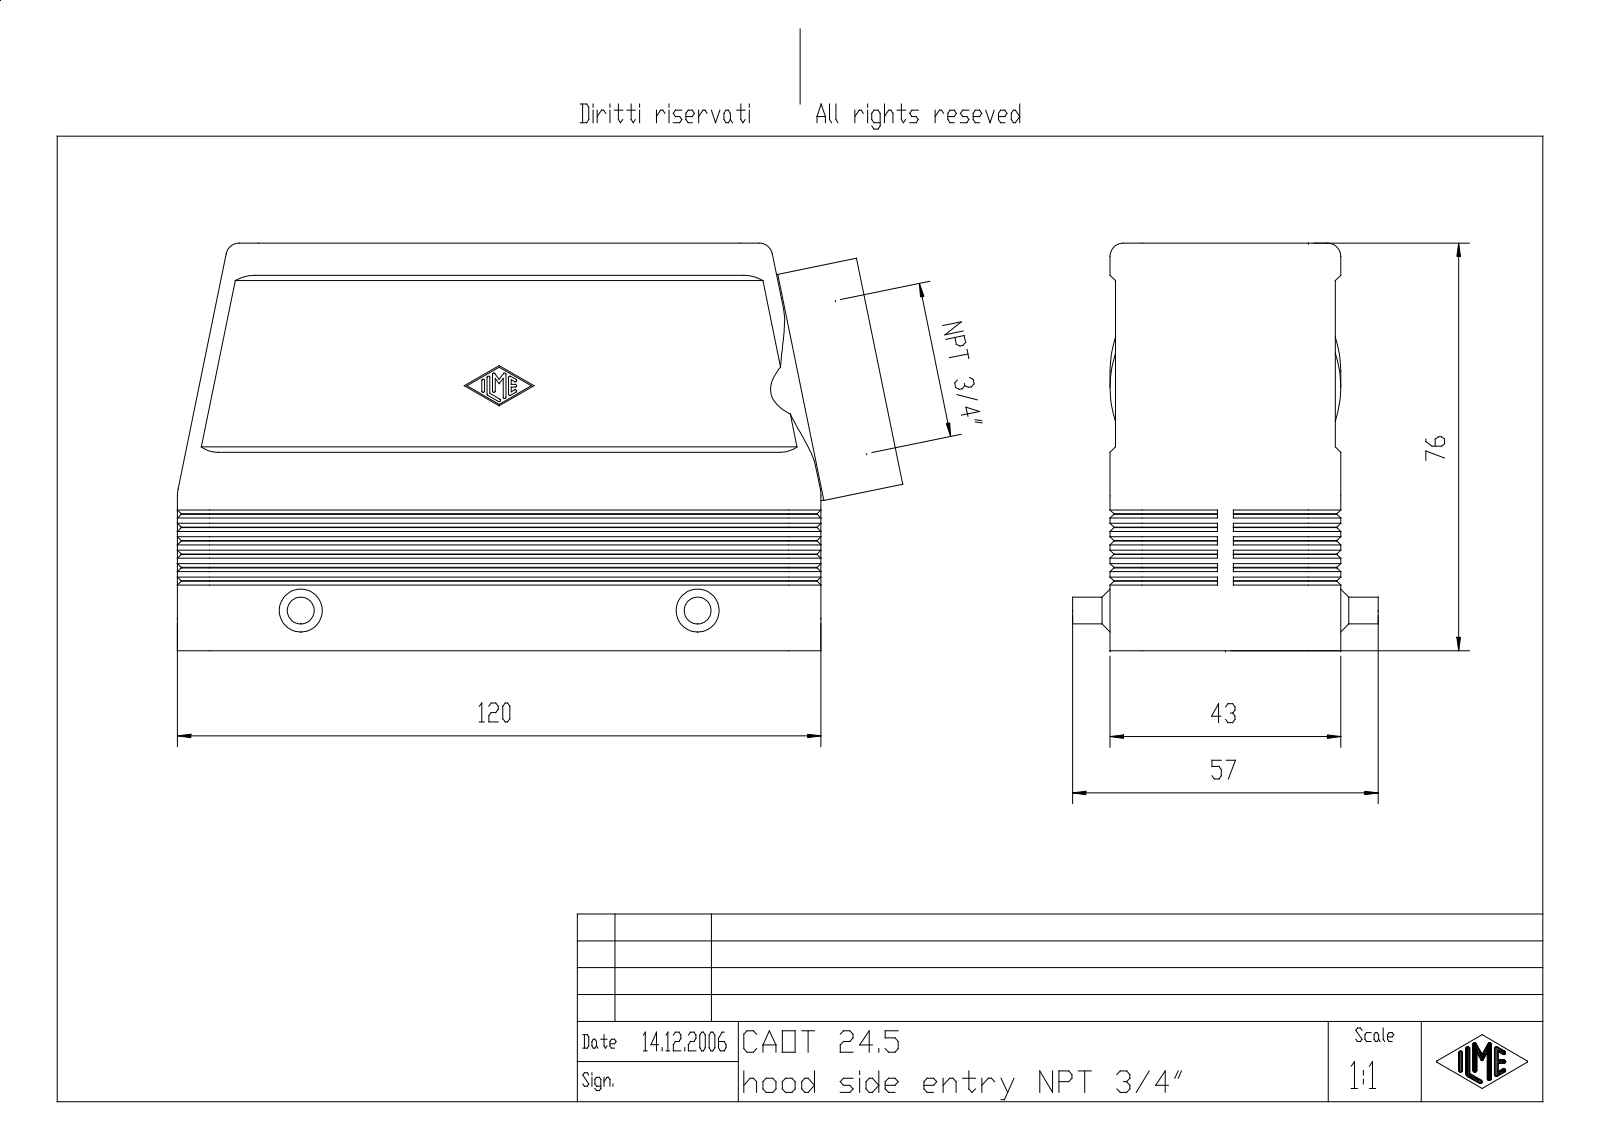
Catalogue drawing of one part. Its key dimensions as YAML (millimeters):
part_name: "MSBO8691"
step_written_by: "Creo Elements/Direct Modeling 18.0B 02-Dec-2011 (C) Parametric Technology GmbH (AUTOMOTIVE_DESIGN)"
units: millimeters
bodies: {solids: 1, faces: 422, planar: 228, cylindrical: 116, other: 78}
overall_size: [135.24, 76, 57]
volume: 100097
surface_area: 57750
round_holes:
  - {diameter: 4, count: 4}
  - {diameter: 2.46, count: 3}
  - {diameter: 2.46, count: 1}
round_bosses_or_shafts:
  - {diameter: 5, count: 2}
  - {diameter: 43, count: 1}
partial_cylinders:
  - {radius: 0.25, count: 14}
  - {radius: 6, count: 12}
  - {radius: 2, count: 4}
  - {radius: 2.5, count: 4}
  - {radius: 3, count: 4}
  - {radius: 5.3, count: 4}
  - {radius: 13.89, count: 1}
face_to_face_distances: [3, 37, 2, 40, 39, 1, 42, 43, 41, 1.77]
hole_center_spacings: [27, 104, 107.45]
